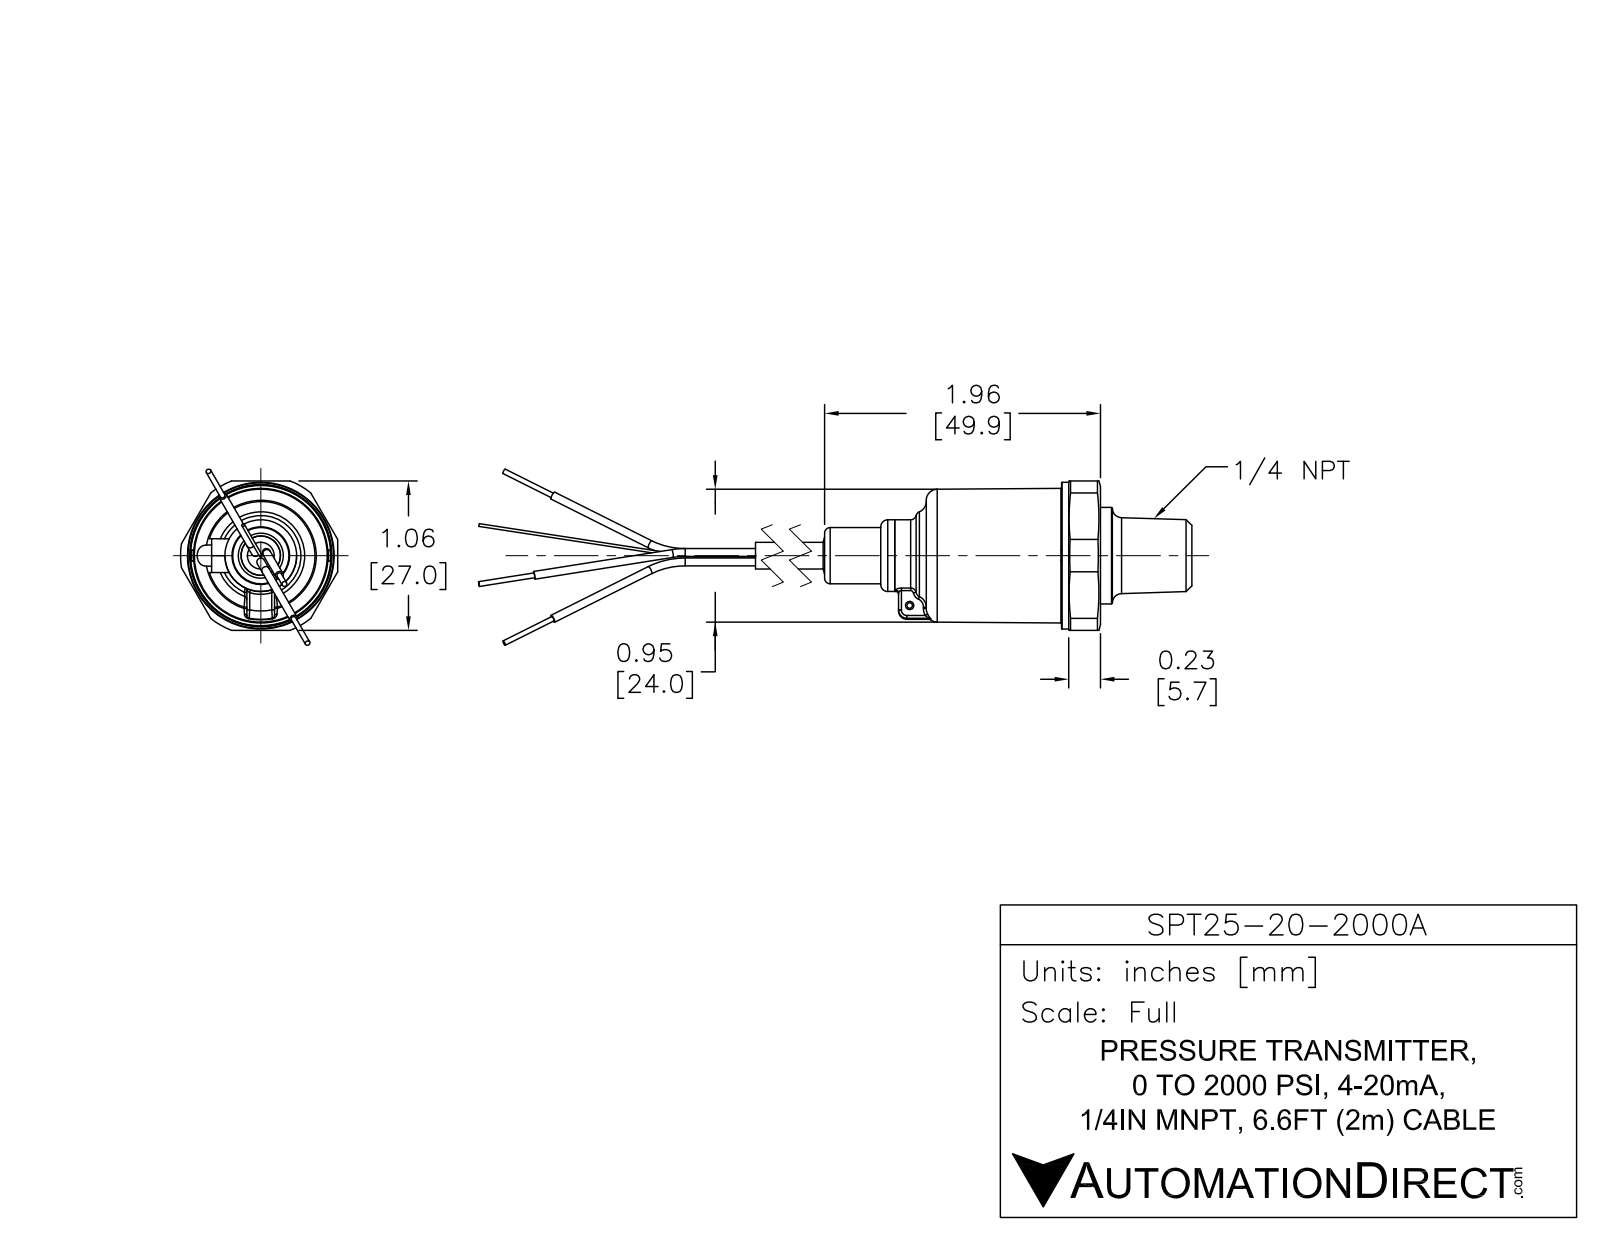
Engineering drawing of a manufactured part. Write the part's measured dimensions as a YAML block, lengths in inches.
part_name: "SPT25-20-2000A"
step_written_by: "SolidWorks 2017 (AUTOMOTIVE_DESIGN)"
units: inches
bodies: {solids: 7, faces: 116, planar: 32, cylindrical: 49, other: 35}
overall_size: [6.035, 1.142, 1.067]
volume: 1.269
surface_area: 11.11
round_holes:
  - {diameter: 0.039, count: 1}
  - {diameter: 0.13, count: 1}
round_bosses_or_shafts:
  - {diameter: 0.055, count: 6}
  - {diameter: 0.03, count: 5}
  - {diameter: 1.053, count: 1}
  - {diameter: 0.945, count: 1}
  - {diameter: 0.689, count: 1}
  - {diameter: 0.551, count: 1}
  - {diameter: 0.512, count: 1}
  - {diameter: 0.394, count: 1}
partial_cylinders:
  - {radius: 0.079, count: 1}
  - {radius: 0.571, count: 1}
face_to_face_distances: [0.266, 0.945, 0.679, 1.683, 1.949, 2.628, 1.732, 0.049, 0.217, 0.896]
